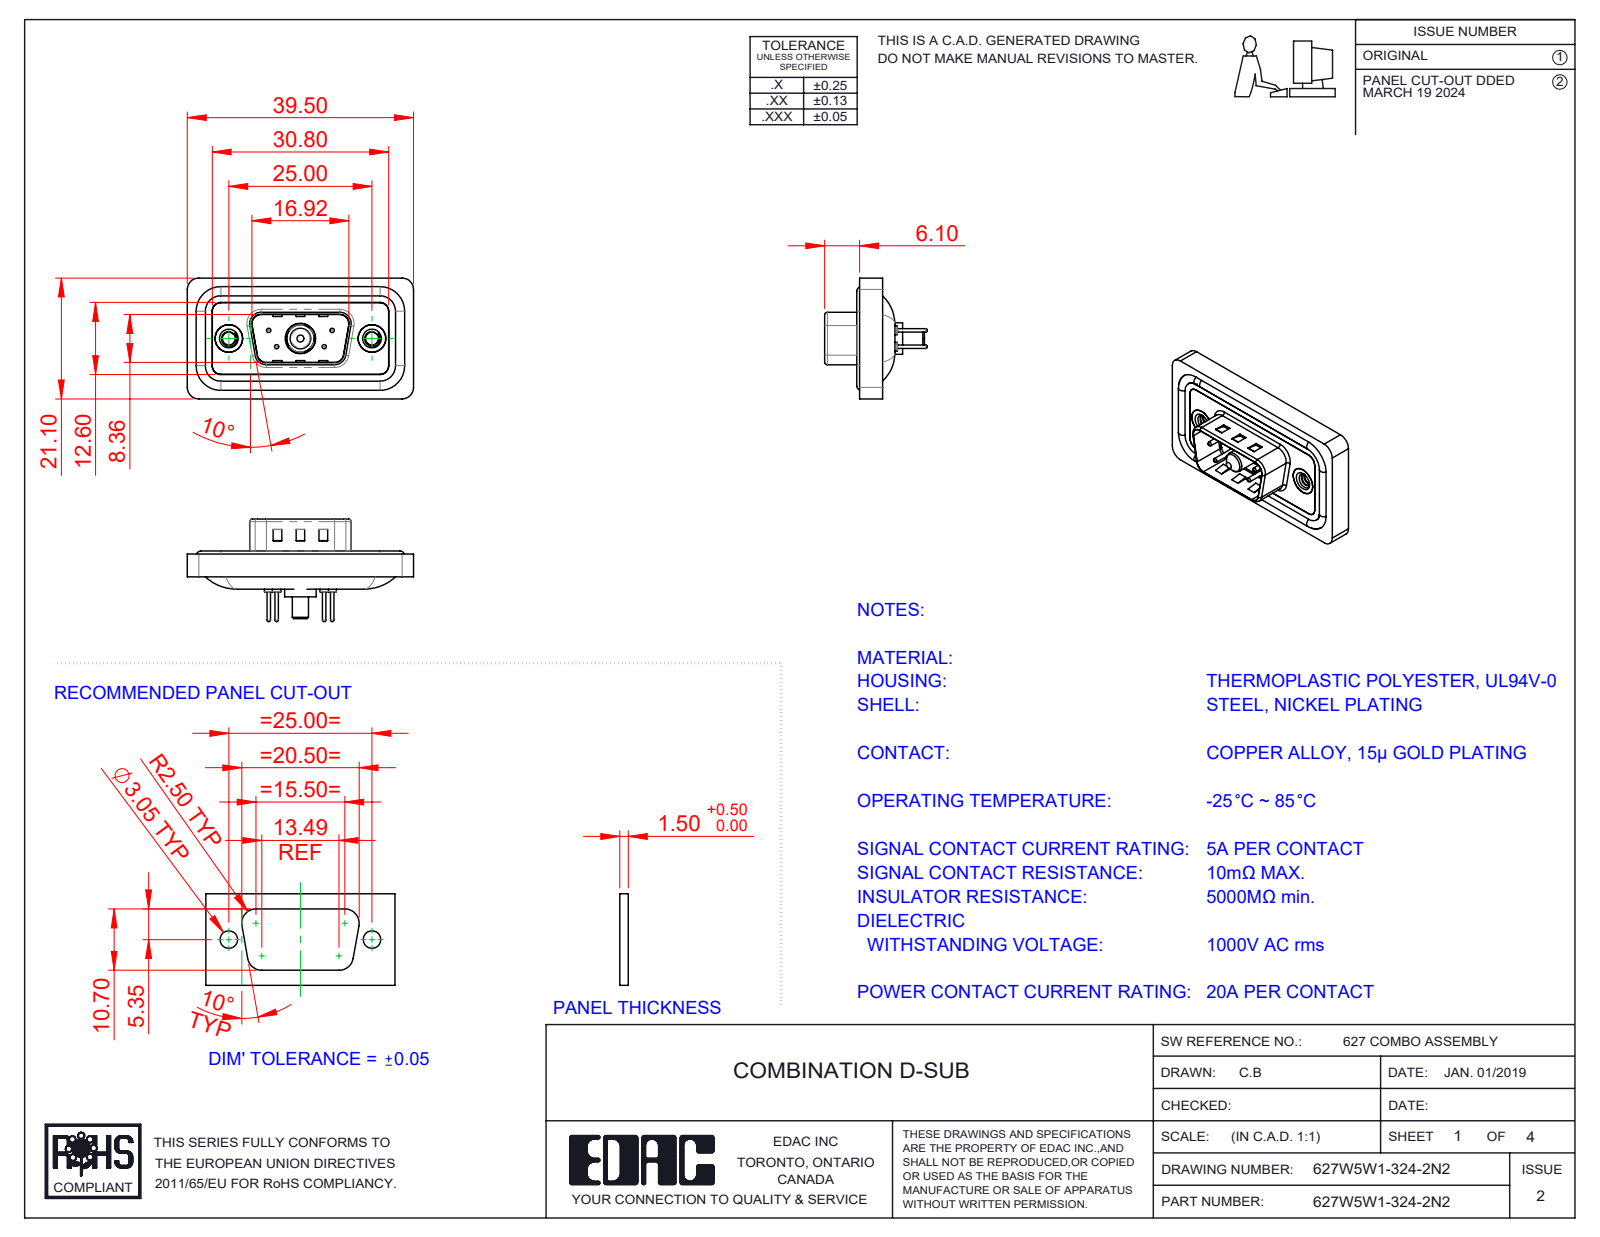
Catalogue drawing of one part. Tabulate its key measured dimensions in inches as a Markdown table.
| quantity | value |
| --- | --- |
| part name | 627Combo Waterproof Housing_09 Contacts; 627W5W1-324-2N2; 627Combo Shell Front_09 Contacts; Power Pin_20A S (+5 more) |
| STEP written by | SolidWorks 2023 (CONFIG_CONTROL_DESIGN) |
| units | inches |
| bodies | 13 solids, 598 faces (183 planar, 255 cylindrical, 160 other) |
| overall size | 1.555 × 0.831 × 0.705 |
| volume | 0.268 in³ |
| surface area | 10.76 in² |
| round holes (diameter × count) | 0.03 × 4, 0.063 × 4, 0.079 × 4, 0.089 × 2, 0.157 × 2, 0.189 × 2, 0.197 × 2, 0.191 × 1, 0.209 × 1 |
| round bosses / shafts (diameter × count) | 0.063 × 4, 0.059 × 4, 0.024 × 4, 0.193 × 2, 0.217 × 1, 0.205 × 1, 0.187 × 1, 0.148 × 1 |
| partial cylindrical surfaces (radius × count) | 0.059 × 22, 0.079 × 18, 0.02 × 8, 0.063 × 8, 0.01 × 4, 0.024 × 4, 0.026 × 4, 0.035 × 4 |
| main face-to-face distances | 0.016, 0.043, 0.114, 0.063, 0.059, 0.122, 0.02, 0.098, 0.157, 0.031 |
| hole center spacings | 0.124, 0.225, 0.28, 0.492, 0.713, 0.173, 0.173, 0.327 |
